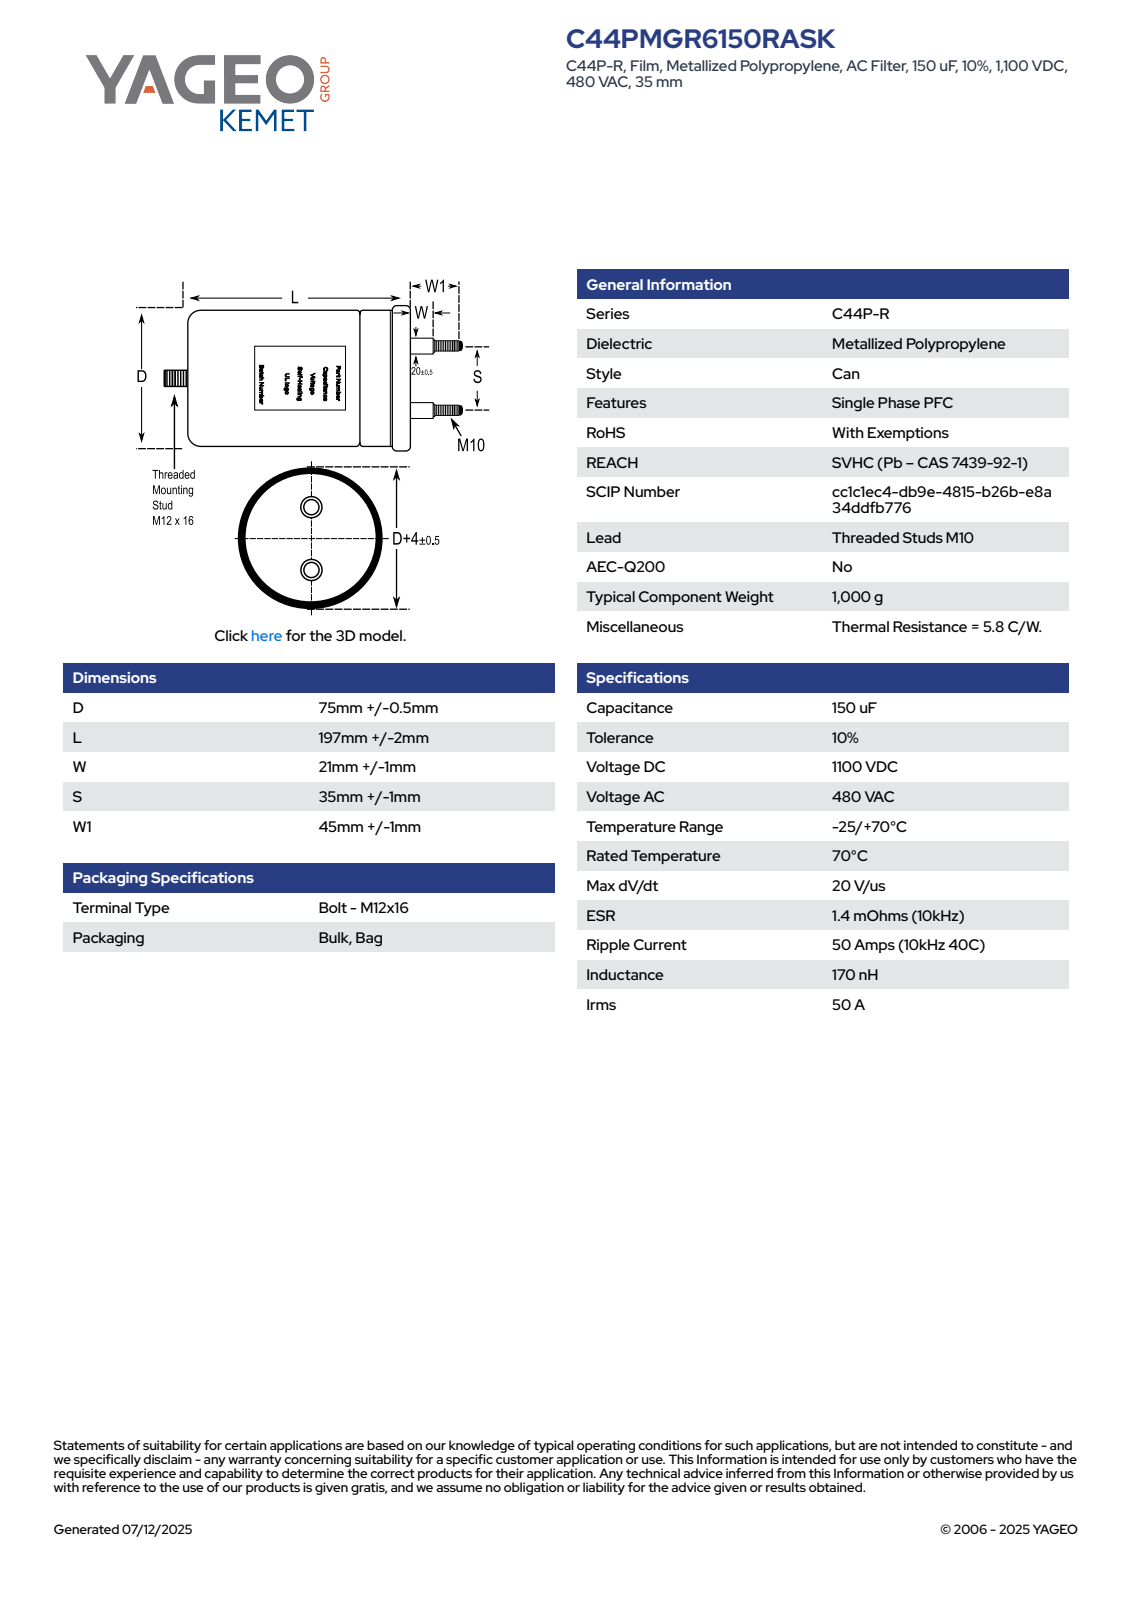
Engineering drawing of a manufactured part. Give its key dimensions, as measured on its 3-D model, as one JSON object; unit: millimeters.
{"part_name": "CFP_C44P_75X197_D75.5L199S35", "step_written_by": "SolidWorks 2014 (AUTOMOTIVE_DESIGN)", "units": "millimeters", "bodies": {"solids": 1, "faces": 105, "planar": 32, "cylindrical": 36, "other": 37}, "overall_size": [261, 80, 80], "volume_mm3": 912756, "surface_area_mm2": 61502, "round_bosses_or_shafts": [[12, 3], [20.5, 2], [10, 2], [80, 1], [75.5, 1]], "partial_cylinders_radius": [[37.76, 1]], "face_to_face_distances": [199, 220, 21, 192.61, 6.39, 27.39, 245, 52.39, 46, 25]}
